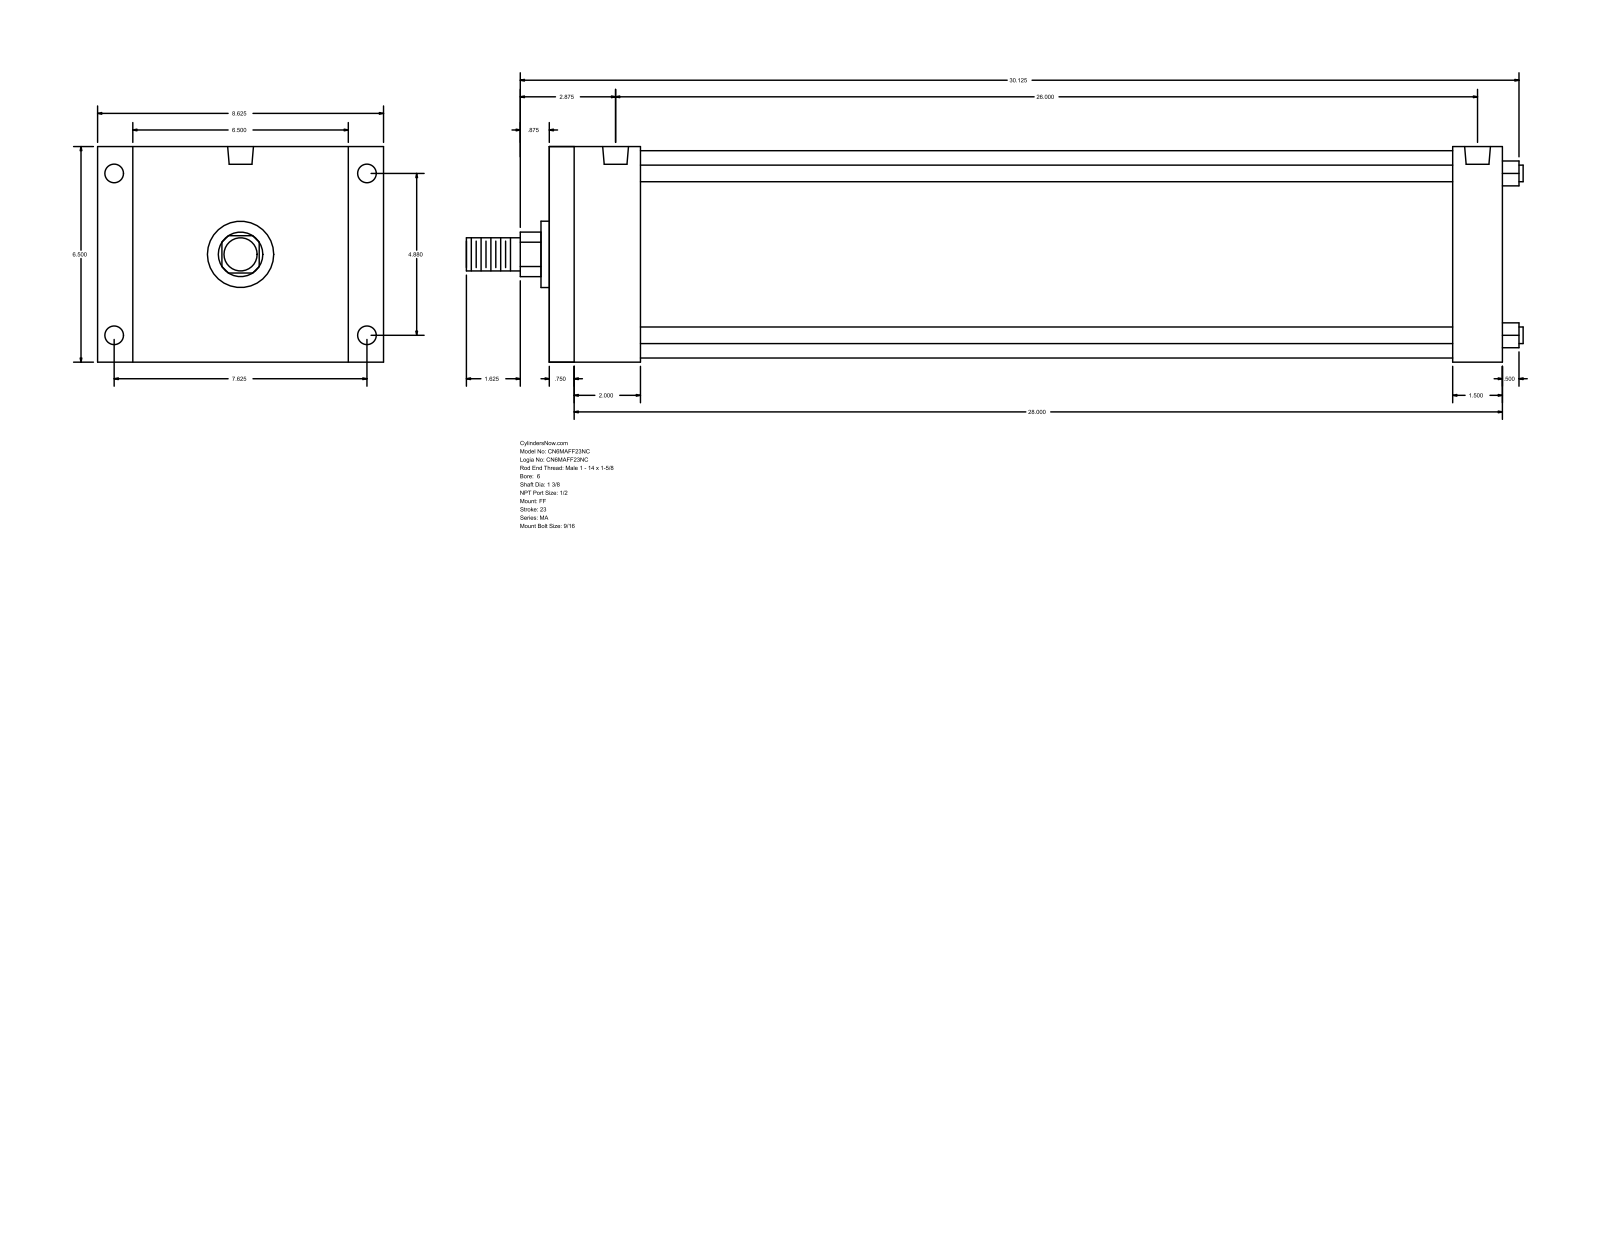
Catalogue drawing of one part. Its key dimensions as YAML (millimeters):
part_name: "MA_FF__0600_1.375"
step_written_by: "GSSL Pune (CONFIG_CONTROL_DESIGN)"
units: millimeters
bodies: {solids: 0, faces: 92, planar: 64, cylindrical: 28, other: 0}
overall_size: [809.62, 219.07, 165.1]
round_holes:
  - {diameter: 14.29, count: 4}
  - {diameter: 17.46, count: 4}
  - {diameter: 19.77, count: 2}
round_bosses_or_shafts:
  - {diameter: 12.7, count: 4}
  - {diameter: 158.75, count: 1}
  - {diameter: 50.8, count: 1}
  - {diameter: 34.92, count: 1}
  - {diameter: 25.4, count: 1}
partial_cylinders:
  - {radius: 17.06, count: 1}
face_to_face_distances: [165.1, 730.25, 15.87, 714.38, 38.1, 66.67, 50.8, 663.58, 692.15, 676.28]
hole_center_spacings: [123.96, 193.68, 229.95, 663.57, 3.18, 660.39]
